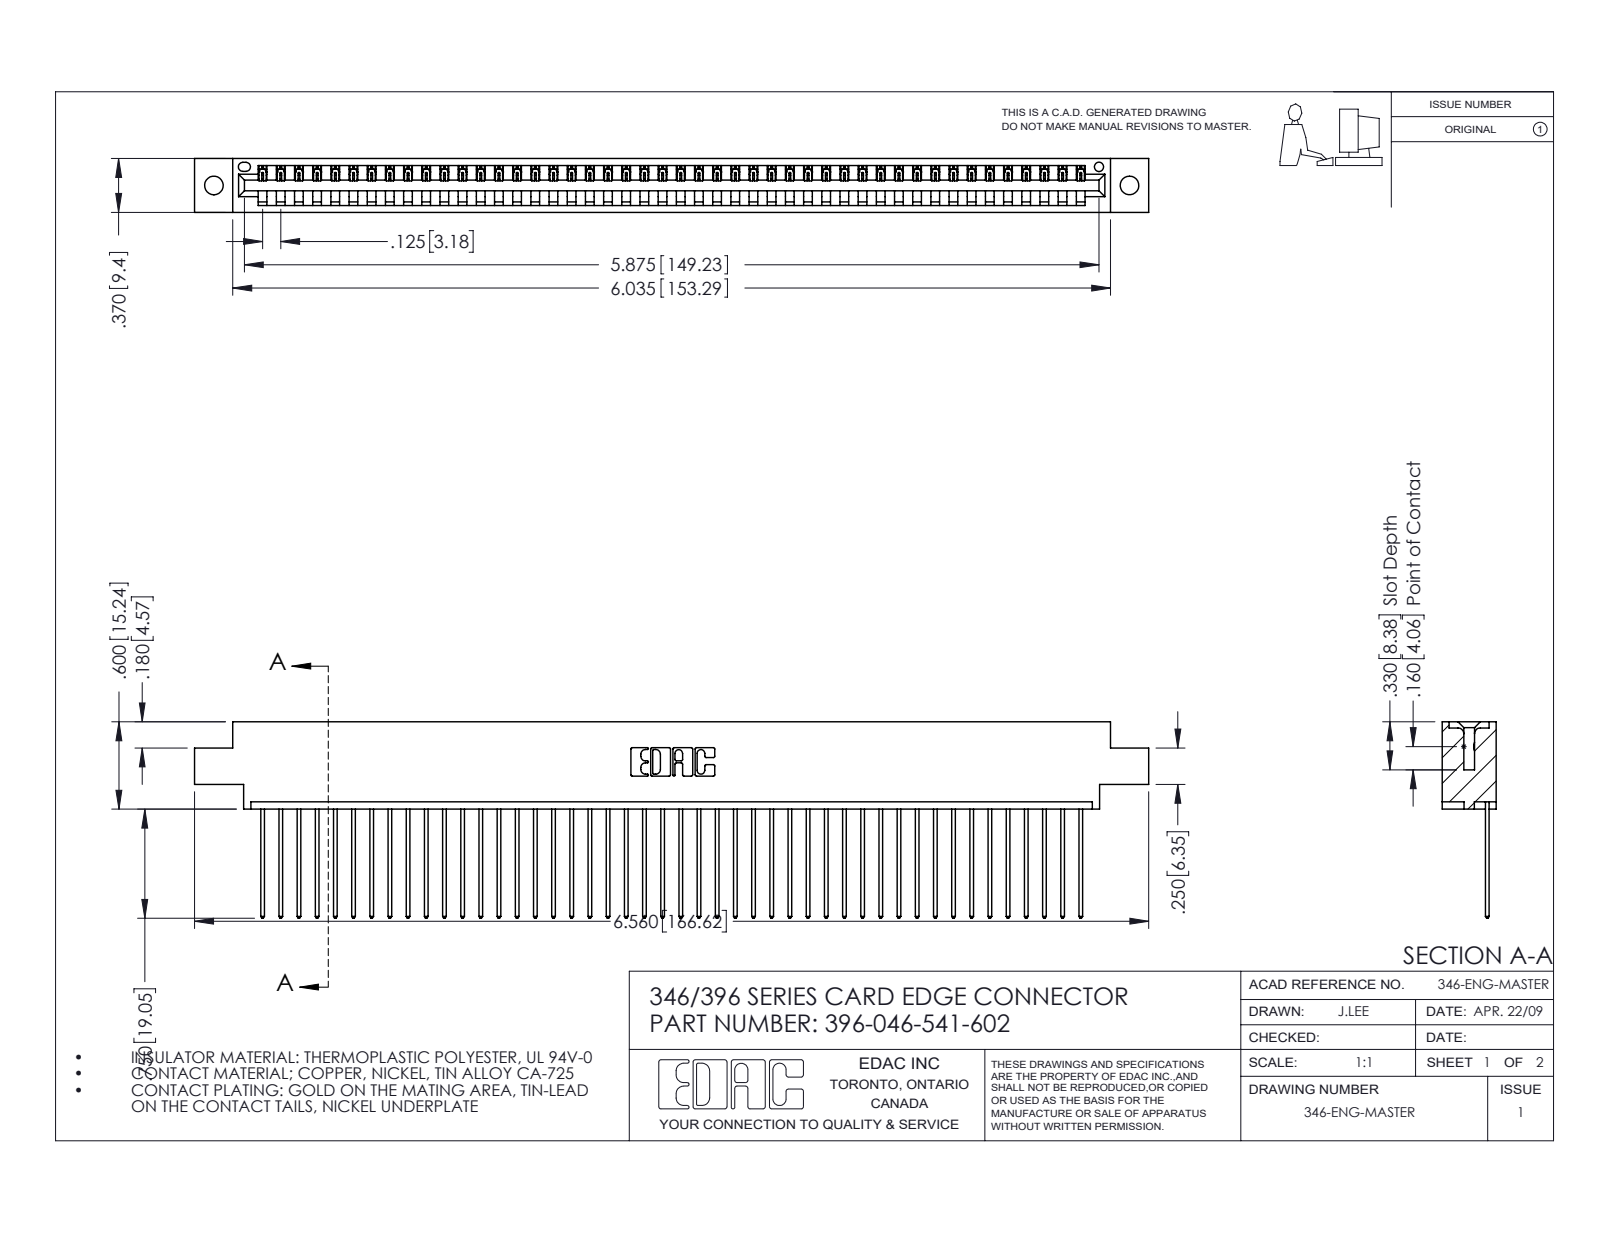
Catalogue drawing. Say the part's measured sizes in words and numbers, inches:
The part is named "345-292-001_345-293-141; 396-046-541-602; 346 Part_0.170 Offset - 0.128 Dia". Its 3-D file was written by "SolidWorks 2016 (CONFIG_CONTROL_DESIGN)". It is 47 solids with 2794 faces: 1920 planar, 874 cylindrical and 0 other. Overall it measures 6.56 by 1.35 by 0.37 inches. Its volume is 0.973 cubic inches and its surface area 32.18 square inches. Round holes: 2 of diameter 0.128, 1 of diameter 0.064. Partial cylindrical surfaces (rounded edges, fillets, slot ends): 92 of radius 0.006, 92 of radius 0.01, 22 of radius 0.01, 6 of radius 0.007, 6 of radius 0.031, 3 of radius 0.026, 2 of radius 0.031, 2 of radius 0.04. The main face-to-face distances are 0.048, 0.322, 0.37, 0.25, 0.072, 0.298, 0.025, 0.148, 0.222, 0.1. The hole center spacings are 0.246, 6.086, 6.295.
